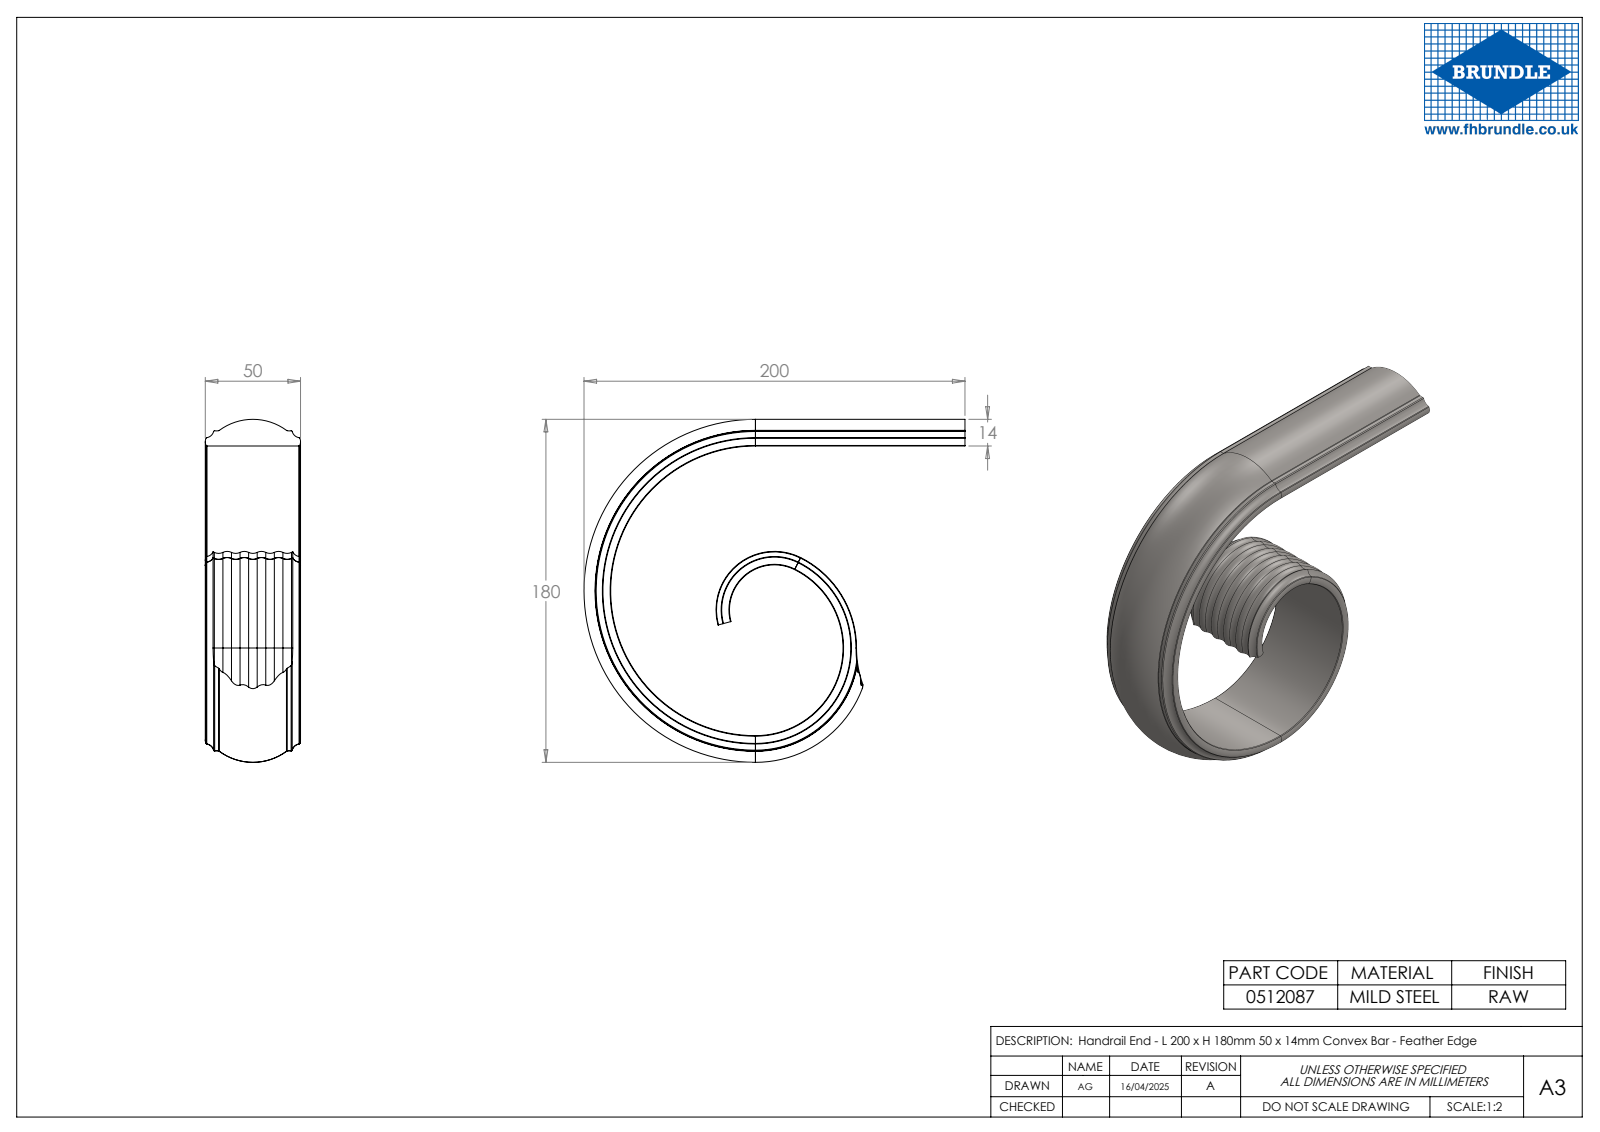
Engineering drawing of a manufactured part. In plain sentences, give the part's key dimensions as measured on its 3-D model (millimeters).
The part is named "0512087". Its 3-D file was written by "SolidWorks 2023 (CONFIG_CONTROL_DESIGN)". It is 4 solids with 123 faces: 9 planar, 22 cylindrical and 92 other. Overall it measures 200 by 180 by 50 millimeters. Its volume is 266 308 cubic millimeters and its surface area 66 471 square millimeters. Partial cylindrical surfaces (rounded edges, fillets, slot ends): 6 of radius 0.5, 2 of radius 1, 2 of radius 4.4, 2 of radius 4.5, 2 of radius 6, 1 of radius 23.64, 1 of radius 29.7, 1 of radius 46. The main face-to-face distances are 110.
